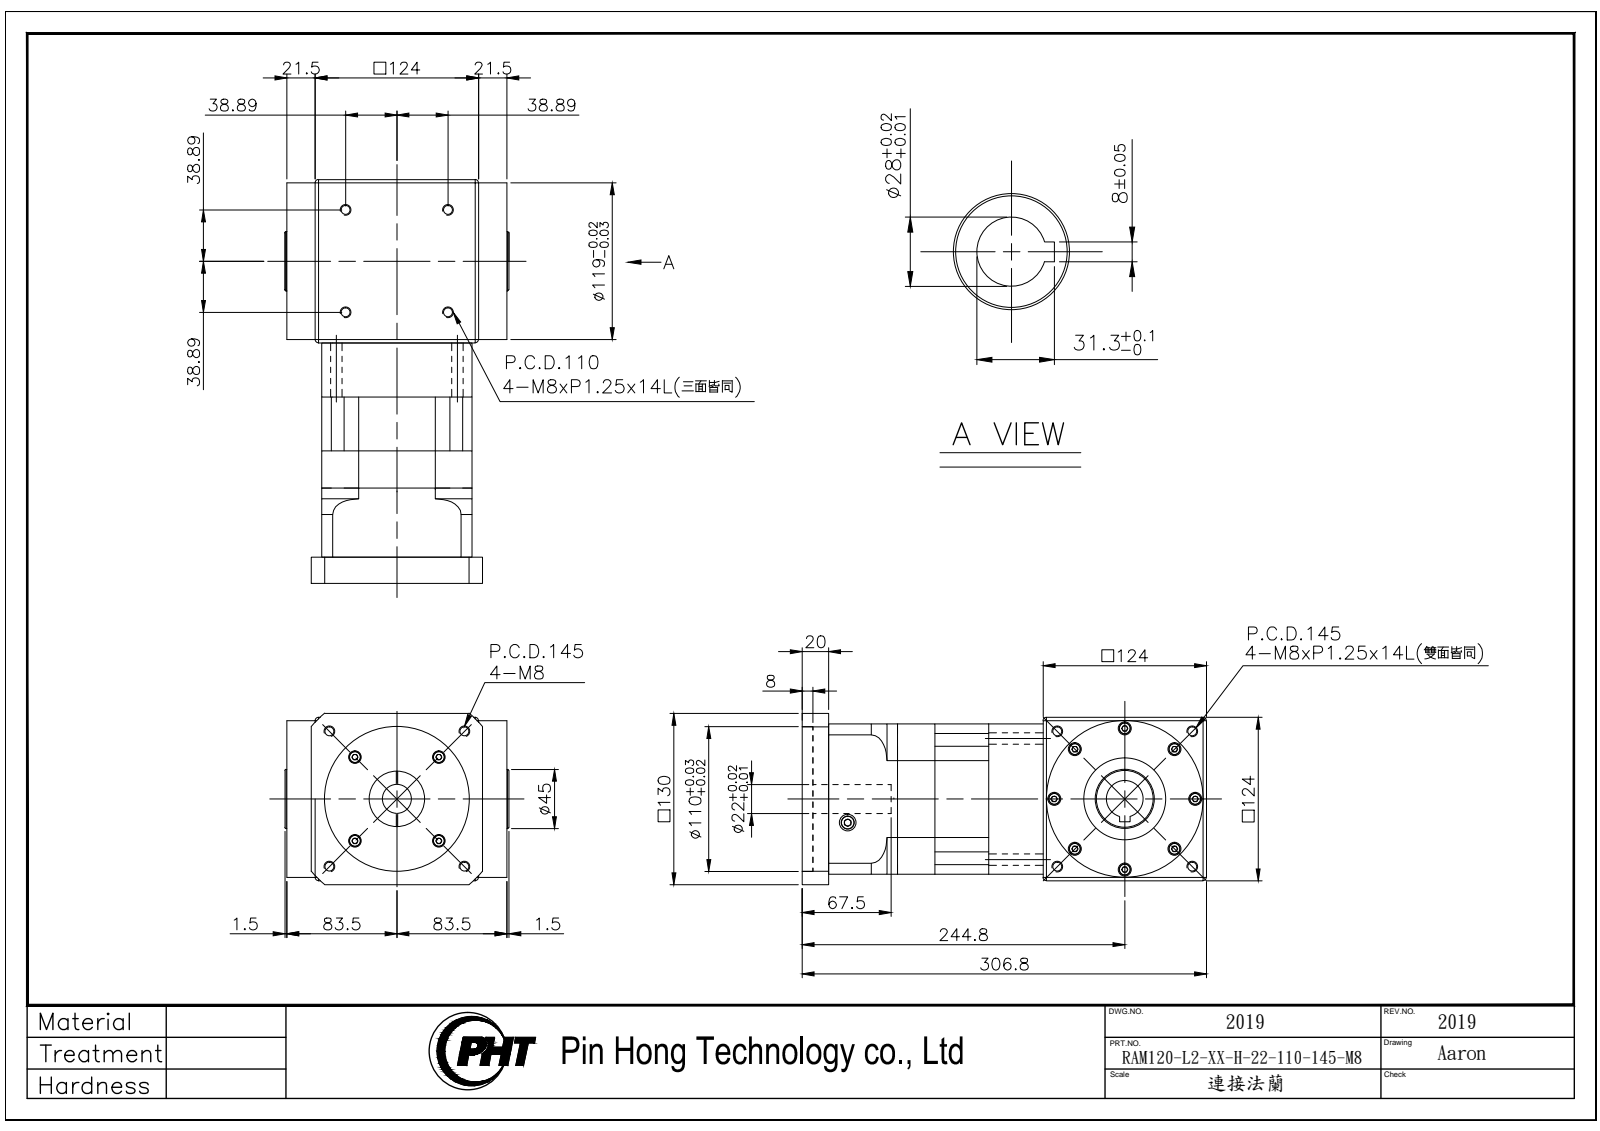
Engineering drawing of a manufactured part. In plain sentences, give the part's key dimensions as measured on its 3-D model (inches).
The part is named "RAM120-L2-XX-H-22-110-145-M8_2019". Its 3-D file was written by "SolidWorks 2016 (AUTOMOTIVE_DESIGN)". It is 5 solids with 865 faces: 417 planar, 300 cylindrical and 148 other. Overall it measures 12.079 by 6.693 by 5.118 inches. Its volume is 267.9 cubic inches and its surface area 602.1 square inches. Round holes: 16 of diameter 0.268, 12 of diameter 0.374, 8 of diameter 0.209, 8 of diameter 0.354, 8 of diameter 0.551, 4 of diameter 0.165, 4 of diameter 0.217, 4 of diameter 0.339, 2 of diameter 0.5, 1 of diameter 0.866, 1 of diameter 1.102, 1 of diameter 1.114. Round bosses or shafts: 12 of diameter 0.512, 4 of diameter 0.335, 1 of diameter 4.685, 1 of diameter 2.441, 1 of diameter 1.929, 1 of diameter 1.772. Partial cylindrical surfaces (rounded edges, fillets, slot ends): 4 of radius 0.276, 1 of radius 2.52, 1 of radius 2.953, 1 of radius 3.346, 1 of radius 3.394. The main face-to-face distances are 0.197, 4.685, 4.882, 4.488, 2.736, 1.114, 1.622, 0.118, 0.315, 1.614. The hole center spacings are 2.323, 0.394, 0.606, 0.679, 0.765, 0.857, 1.567, 2.019.
